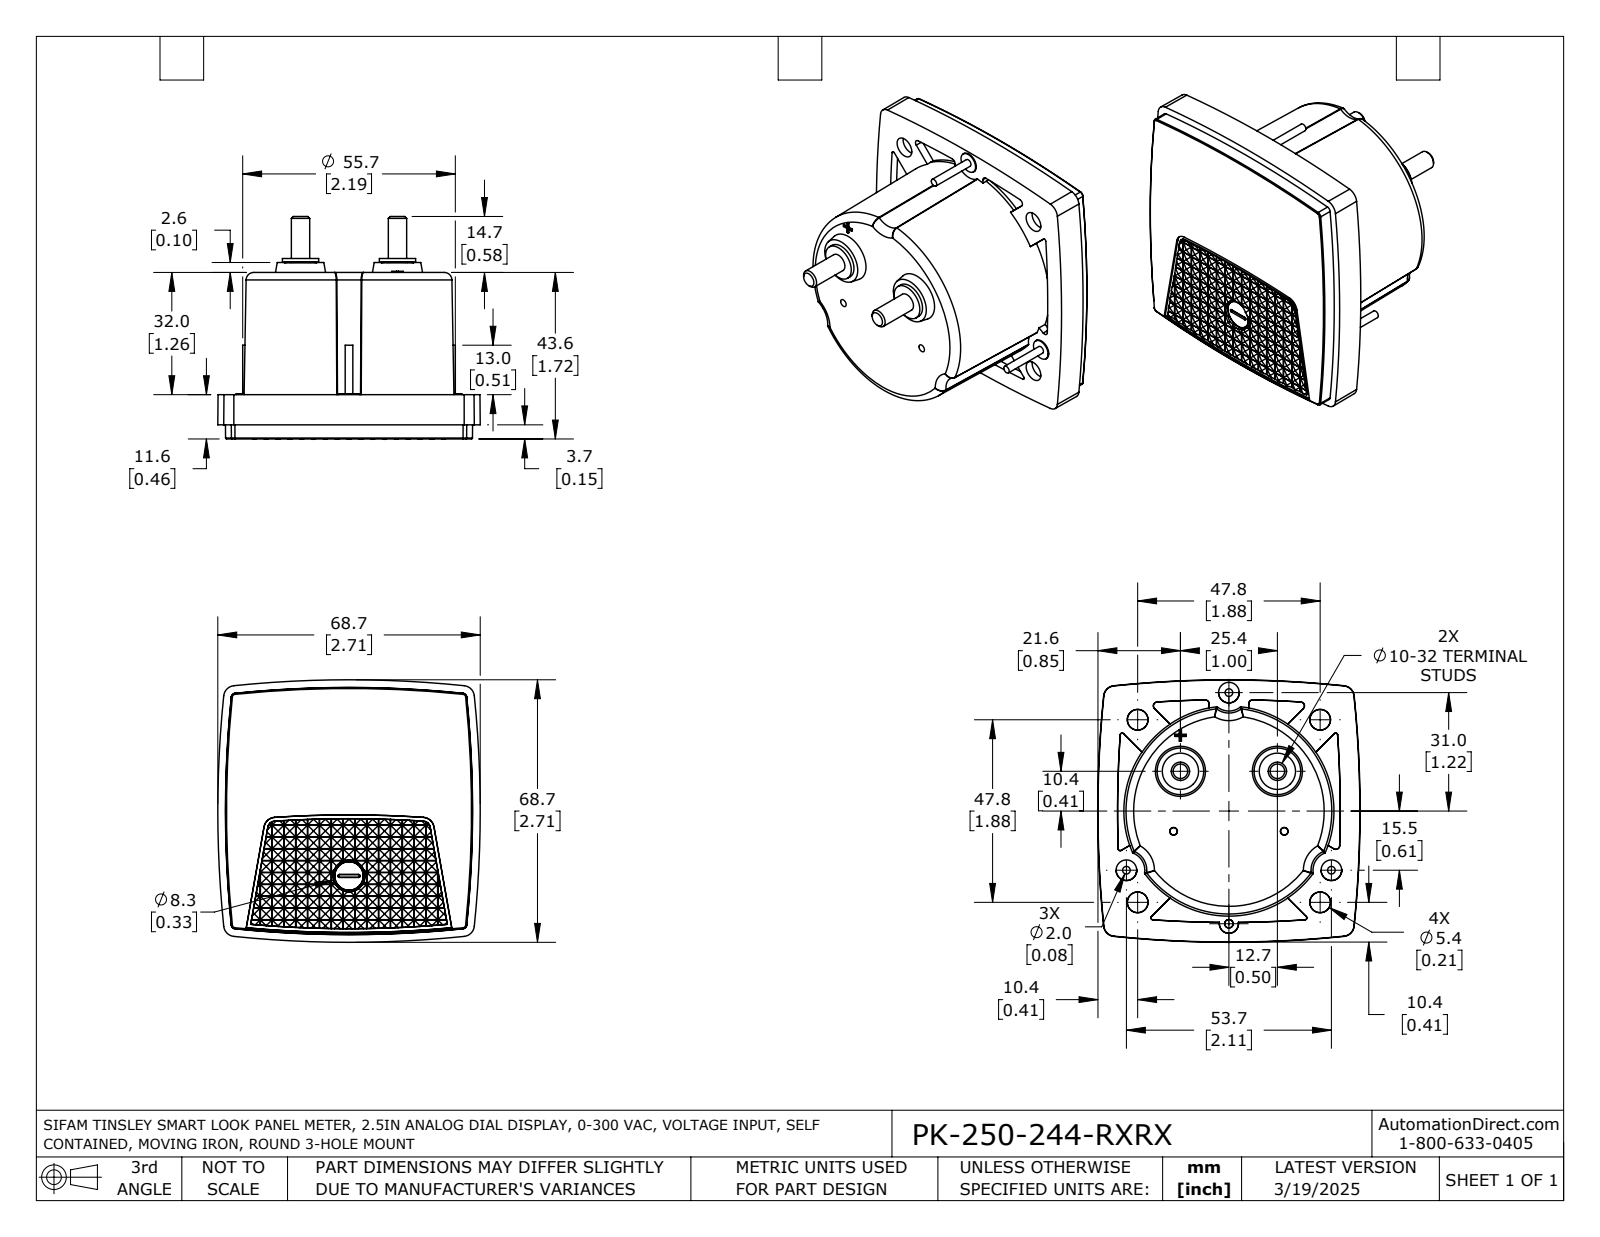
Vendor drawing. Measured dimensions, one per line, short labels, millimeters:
name: PK-250-244-RXRX
written by: SolidWorks 2021 (AUTOMOTIVE_DESIGN)
unit: mm
bodies: 1 solid, 1550 faces (1165 planar, 265 cylindrical, 120 other)
size: 68.7 × 68.7 × 58.3
volume: 124 400 mm³; area: 19 620 mm²
bosses: 3× ⌀5.4, 3× ⌀2, 2× ⌀9.5, 2× ⌀4.8, 1× ⌀5.5
rounds: 2× R4.2, 1× R27.5
face distances: 43.6, 32, 11.6, 0.6, 2.2, 2.4, 7.9, 3, 1.8, 34.2
